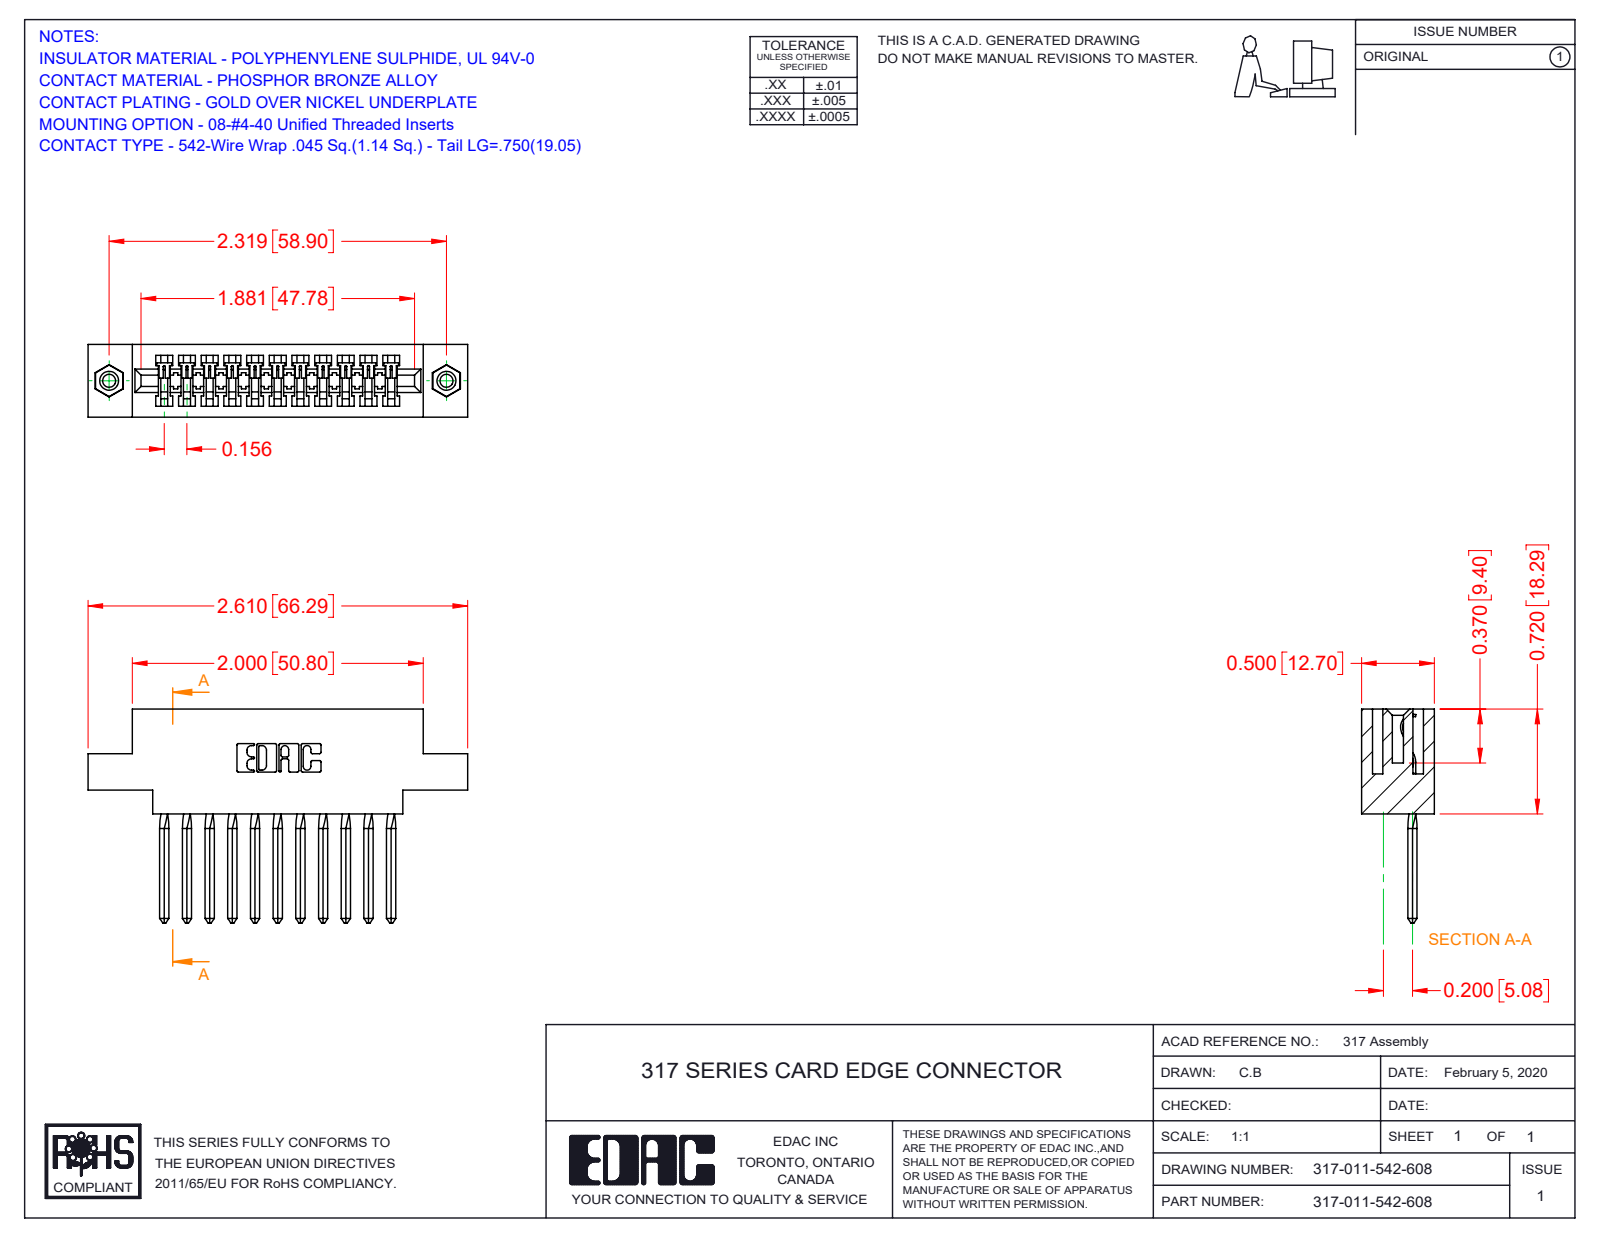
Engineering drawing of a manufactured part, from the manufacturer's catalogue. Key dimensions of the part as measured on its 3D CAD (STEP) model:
Part name (STEP PRODUCT): 345-250-001_345-250-003-102; 317-011-542-608; 317-290-003_542; 317 Part_.156 Dia - TI
STEP written by: SolidWorks 2016 (CONFIG_CONTROL_DESIGN)
Units: inches
Bodies: 14 solids, 987 faces (794 planar, 133 cylindrical, 60 other)
Overall size (bounding box): 2.61 × 1.47 × 0.5
Volume: 0.574 in³ · Surface area: 16.75 in²
Round holes (diameter × count): ⌀0.089 ×2, ⌀0.125 ×2, ⌀0.156 ×2
Round bosses / shafts (diameter × count): ⌀0.155 ×2
Partial cylindrical surfaces — rounded edges, fillets, slot ends (radius × count): R0.006 ×22, R0.01 ×22, R0.007 ×6, R0.031 ×6, R0.026 ×3, R0.074 ×1, R0.089 ×1, R0.1 ×1
Main face-to-face distances: 0.5, 0.075, 0.425, 0.11, 0.065, 0.22, 0.35, 0.136, 0.116, 0.331
Hole centre spacings: 2.319
